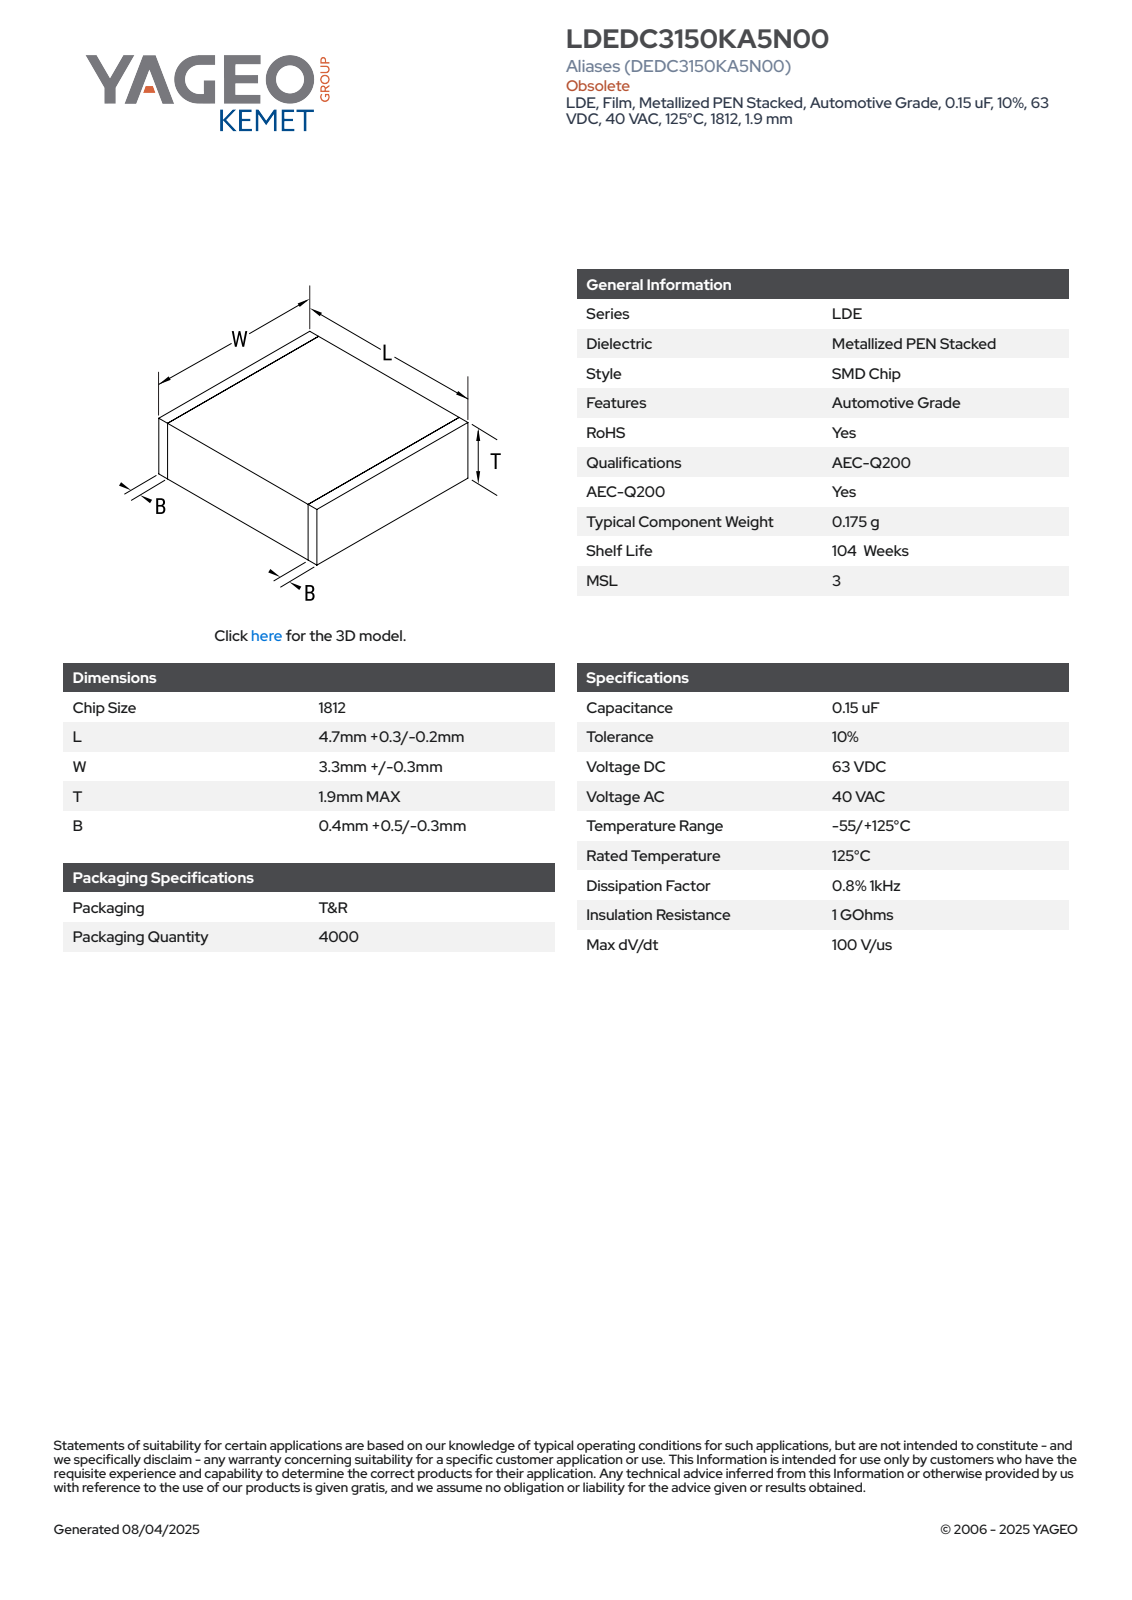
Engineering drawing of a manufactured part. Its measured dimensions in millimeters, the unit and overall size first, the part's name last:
Units: millimetres
Overall size (bounding box): 5 × 3.6 × 1.9
Main face-to-face distances: 1.88, 3.58, 1.89, 5, 3.59, 1.9, 3.6, 0.5, 4.5, 4
Volume: 34 mm³ · Surface area: 70 mm²
Bodies: 4 solids, 73 faces (73 planar, 0 cylindrical, 0 other)
Part name (STEP PRODUCT): CFS_LDELDB_1812_L5W3.6T1.9B0.9
STEP written by: SolidWorks 2020 (AUTOMOTIVE_DESIGN)
